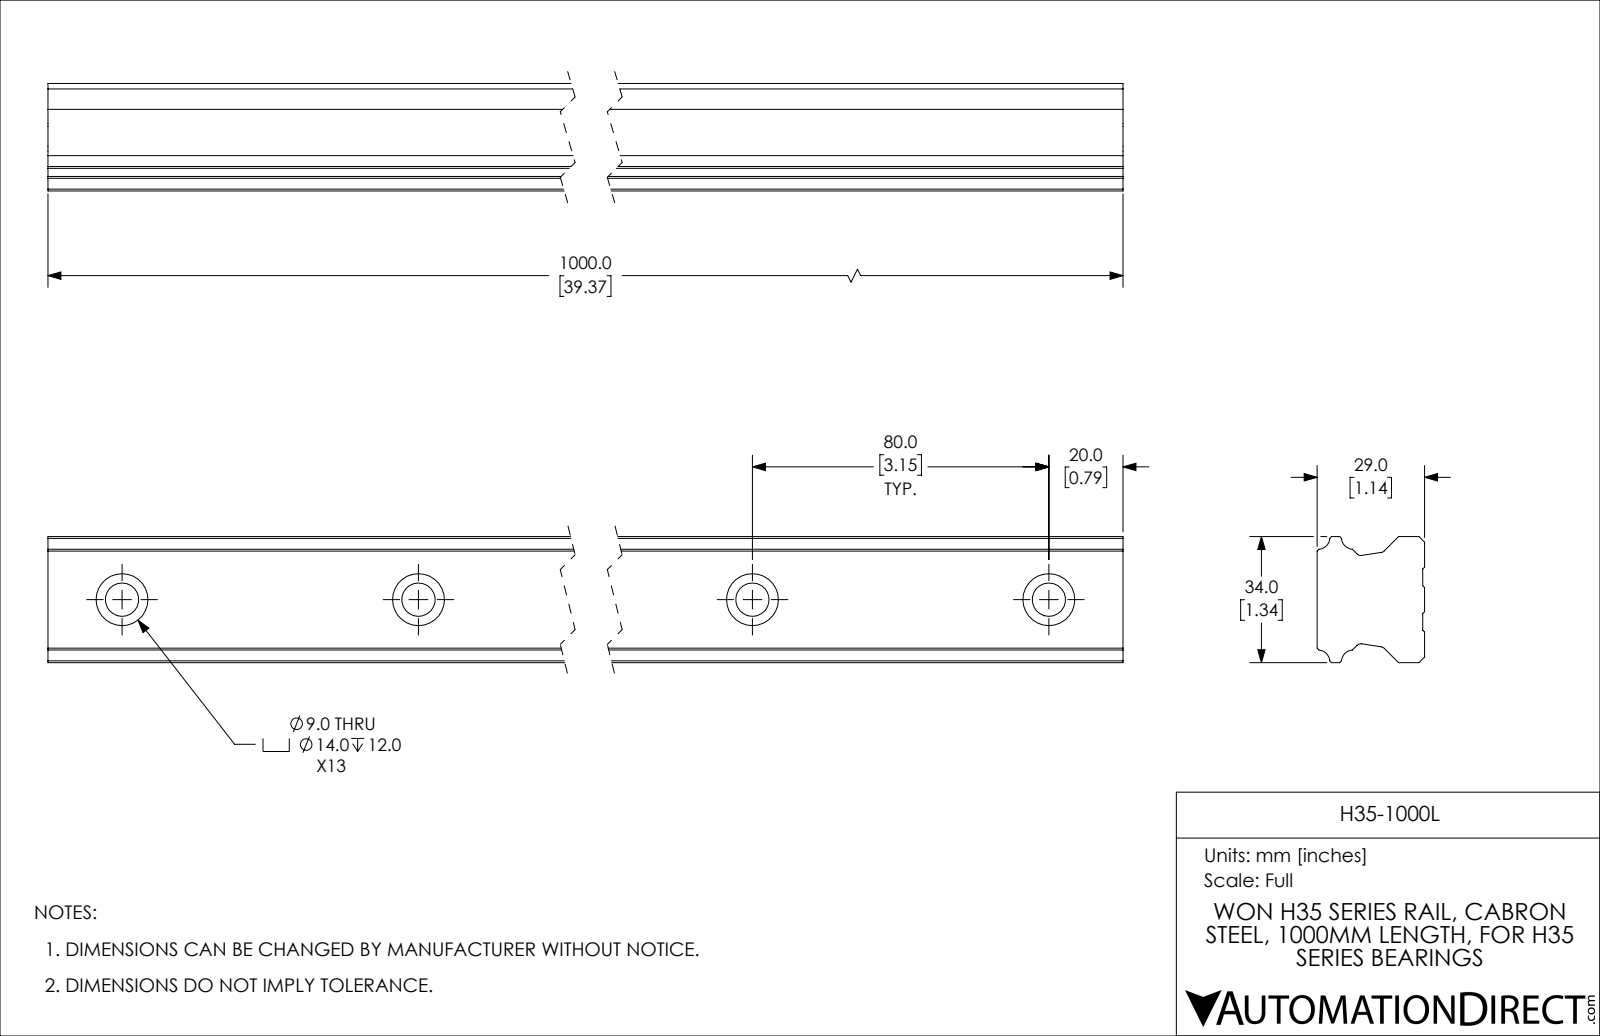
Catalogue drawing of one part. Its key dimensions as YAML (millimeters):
part_name: "H35-1000L"
step_written_by: "SolidWorks 2019 (CONFIG_CONTROL_DESIGN)"
units: millimeters
bodies: {solids: 1, faces: 142, planar: 82, cylindrical: 60, other: 0}
overall_size: [1000, 34, 29]
volume: 811162
surface_area: 142676
round_holes:
  - {diameter: 9, count: 13}
  - {diameter: 14, count: 13}
partial_cylinders:
  - {radius: 1.5, count: 4}
  - {radius: 3.2, count: 4}
face_to_face_distances: [29, 0.5, 28.5, 34, 12.8, 15.13, 27.93, 40.72, 25.59, 12.79]
hole_center_spacings: [80, 160, 240, 320, 400, 480, 560, 640]
